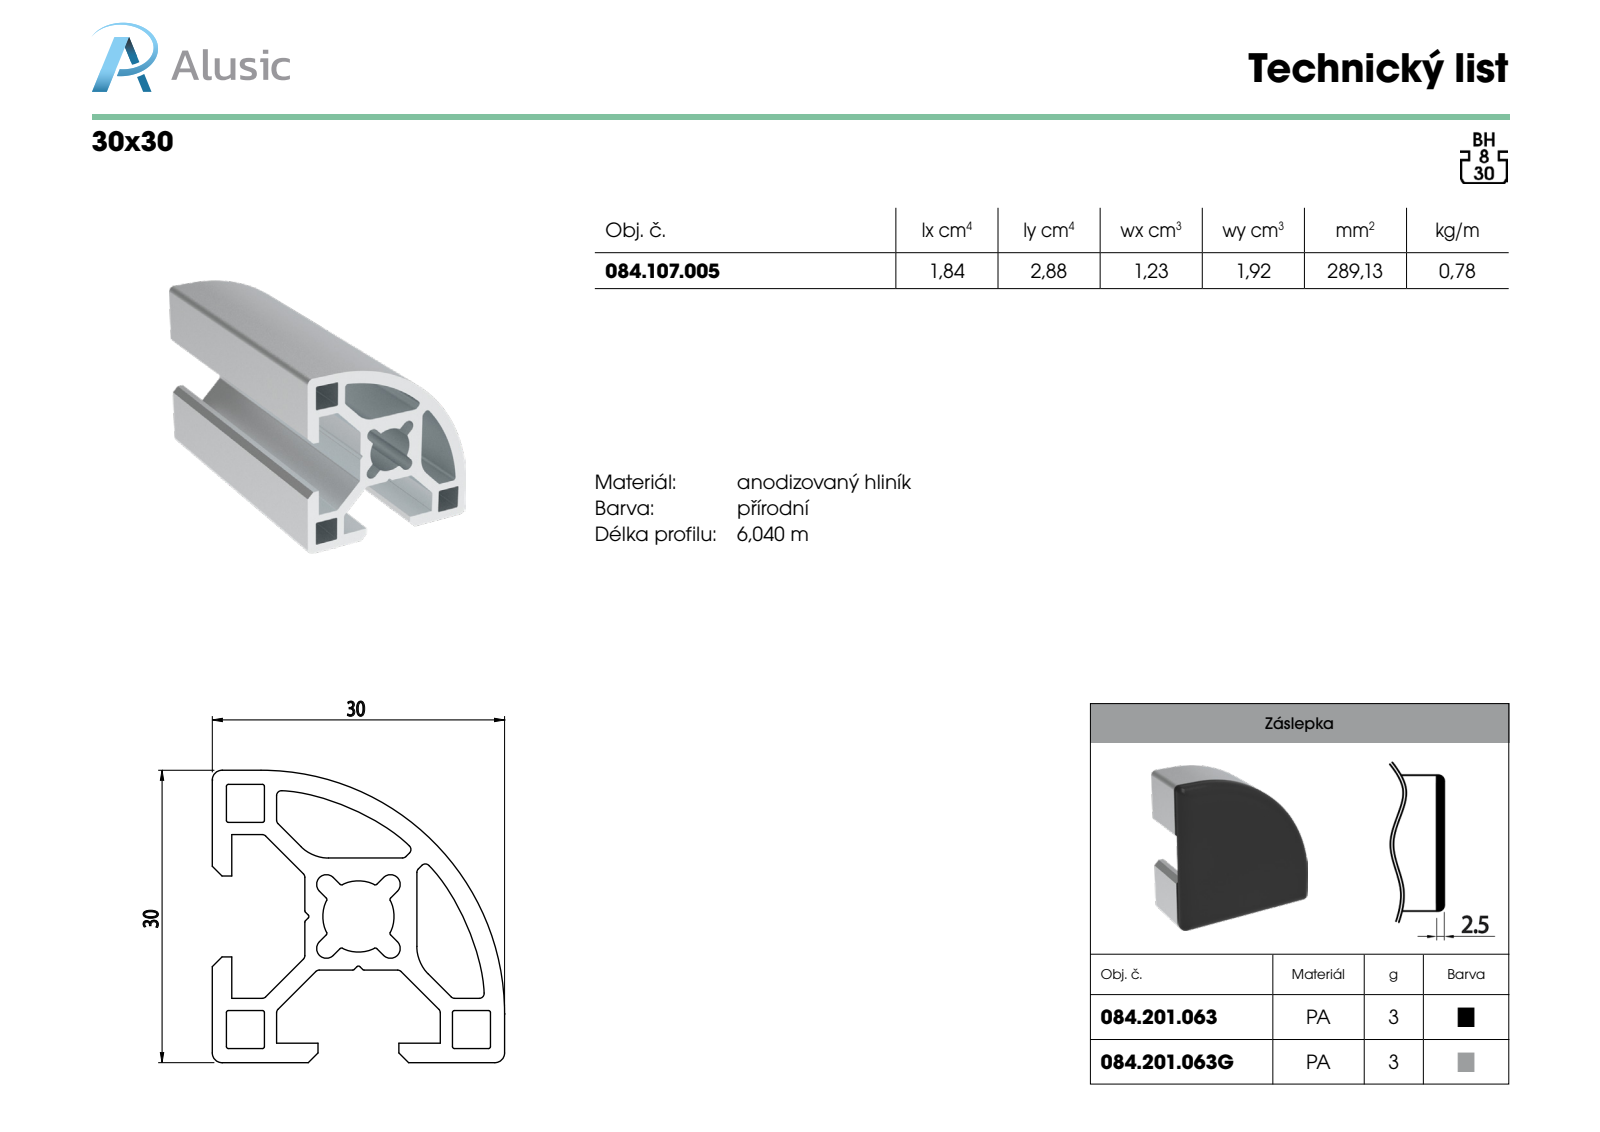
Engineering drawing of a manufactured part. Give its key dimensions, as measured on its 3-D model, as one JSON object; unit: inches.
{"part_name": "084.107.005", "step_written_by": "SolidWorks 2018 (AUTOMOTIVE_DESIGN)", "units": "inches", "bodies": {"solids": 1, "faces": 130, "planar": 64, "cylindrical": 66, "other": 0}, "overall_size": [3.937, 1.181, 1.181], "volume_in3": 1.764, "surface_area_in2": 50.23, "partial_cylinders_radius": [[0.008, 26], [0.02, 16], [0.039, 7], [0.157, 2], [0.144, 1], [0.906, 1], [0.984, 1]], "face_to_face_distances": [0.057, 0.211, 0.154, 0.079, 0.26, 0.203, 0.049, 0.748, 0.827, 1.124]}
